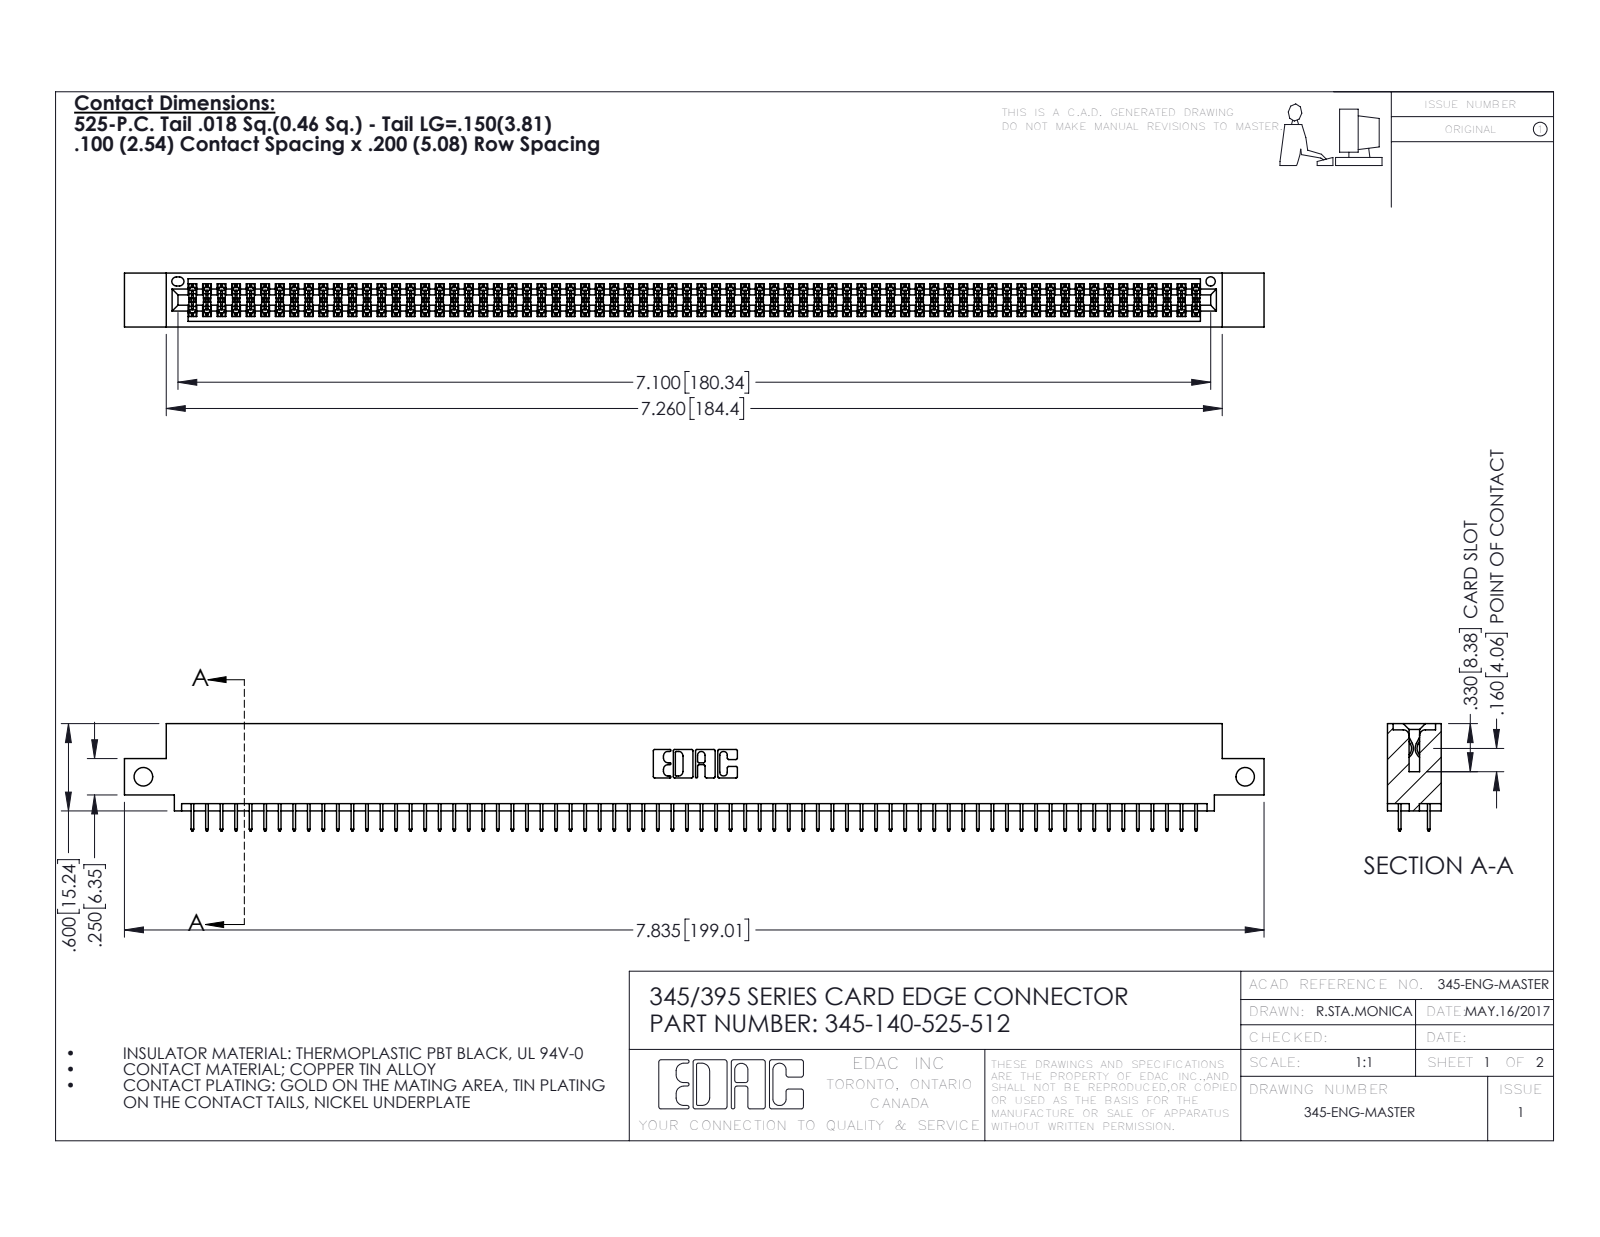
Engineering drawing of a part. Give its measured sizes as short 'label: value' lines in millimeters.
name: 345-292-001_345-293-125; 345-140-525-512; 345 Part_0.110 Offset - Side Mount
written by: SolidWorks 2020 (CONFIG_CONTROL_DESIGN)
unit: mm
bodies: 141 solids, 7690 faces (5544 planar, 2146 cylindrical, 0 other)
size: 199 × 18.7 × 9.4
volume: 19 210 mm³; area: 28 190 mm²
holes: 2× ⌀3.3, 1× ⌀1.6
rounds: 210× R0.2, 22× R0.3, 6× R0.2, 6× R0.8, 3× R0.7, 2× R0.4, 2× R0.5, 2× R0.6
face distances: 1.8, 7.6, 5.1, 9.4, 2.5, 6.9, 0.6, 5.7, 1.8, 4.4
hole spacings: 192.4
